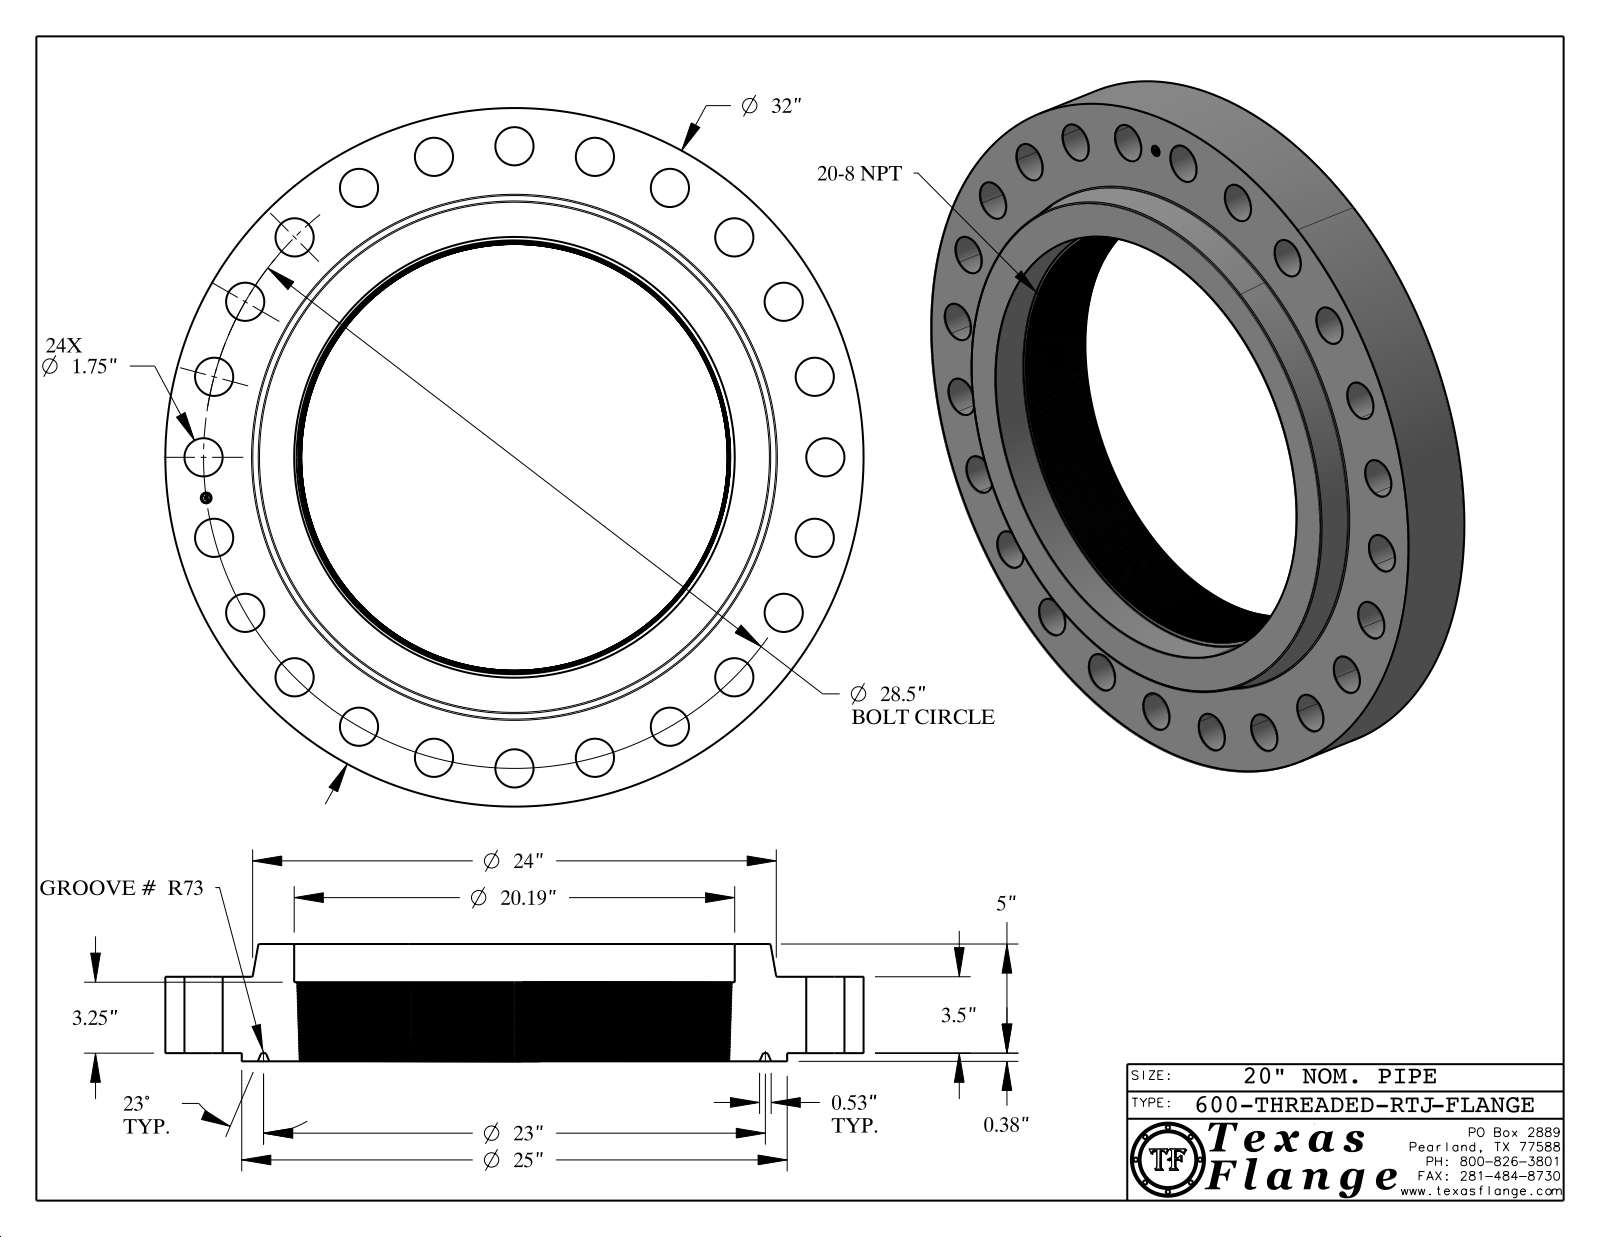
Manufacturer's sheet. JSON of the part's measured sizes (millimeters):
{"part_name": "600-THREADED-RTJ", "step_written_by": "CATIA V5 STEP AP214 (AUTOMOTIVE_DESIGN)", "units": "millimeters", "bodies": {"solids": 1, "faces": 757, "planar": 372, "cylindrical": 74, "other": 311}, "overall_size": [812.8, 812.8, 136.5], "volume_mm3": 29150000, "surface_area_mm2": 1537000, "round_holes": [[44.5, 24], [12.6, 1], [512.8, 1]], "round_bosses_or_shafts": [[0.8, 8], [812.8, 1], [635, 1], [9.9, 1]], "face_to_face_distances": [88.9, 9.5, 98.4, 136.5, 127, 38.1, 92.1, 82.6, 6.4, 44.5], "hole_center_spacings": [362, 94.5, 187.4, 626.9, 668.8, 699.2, 511.9, 277]}
